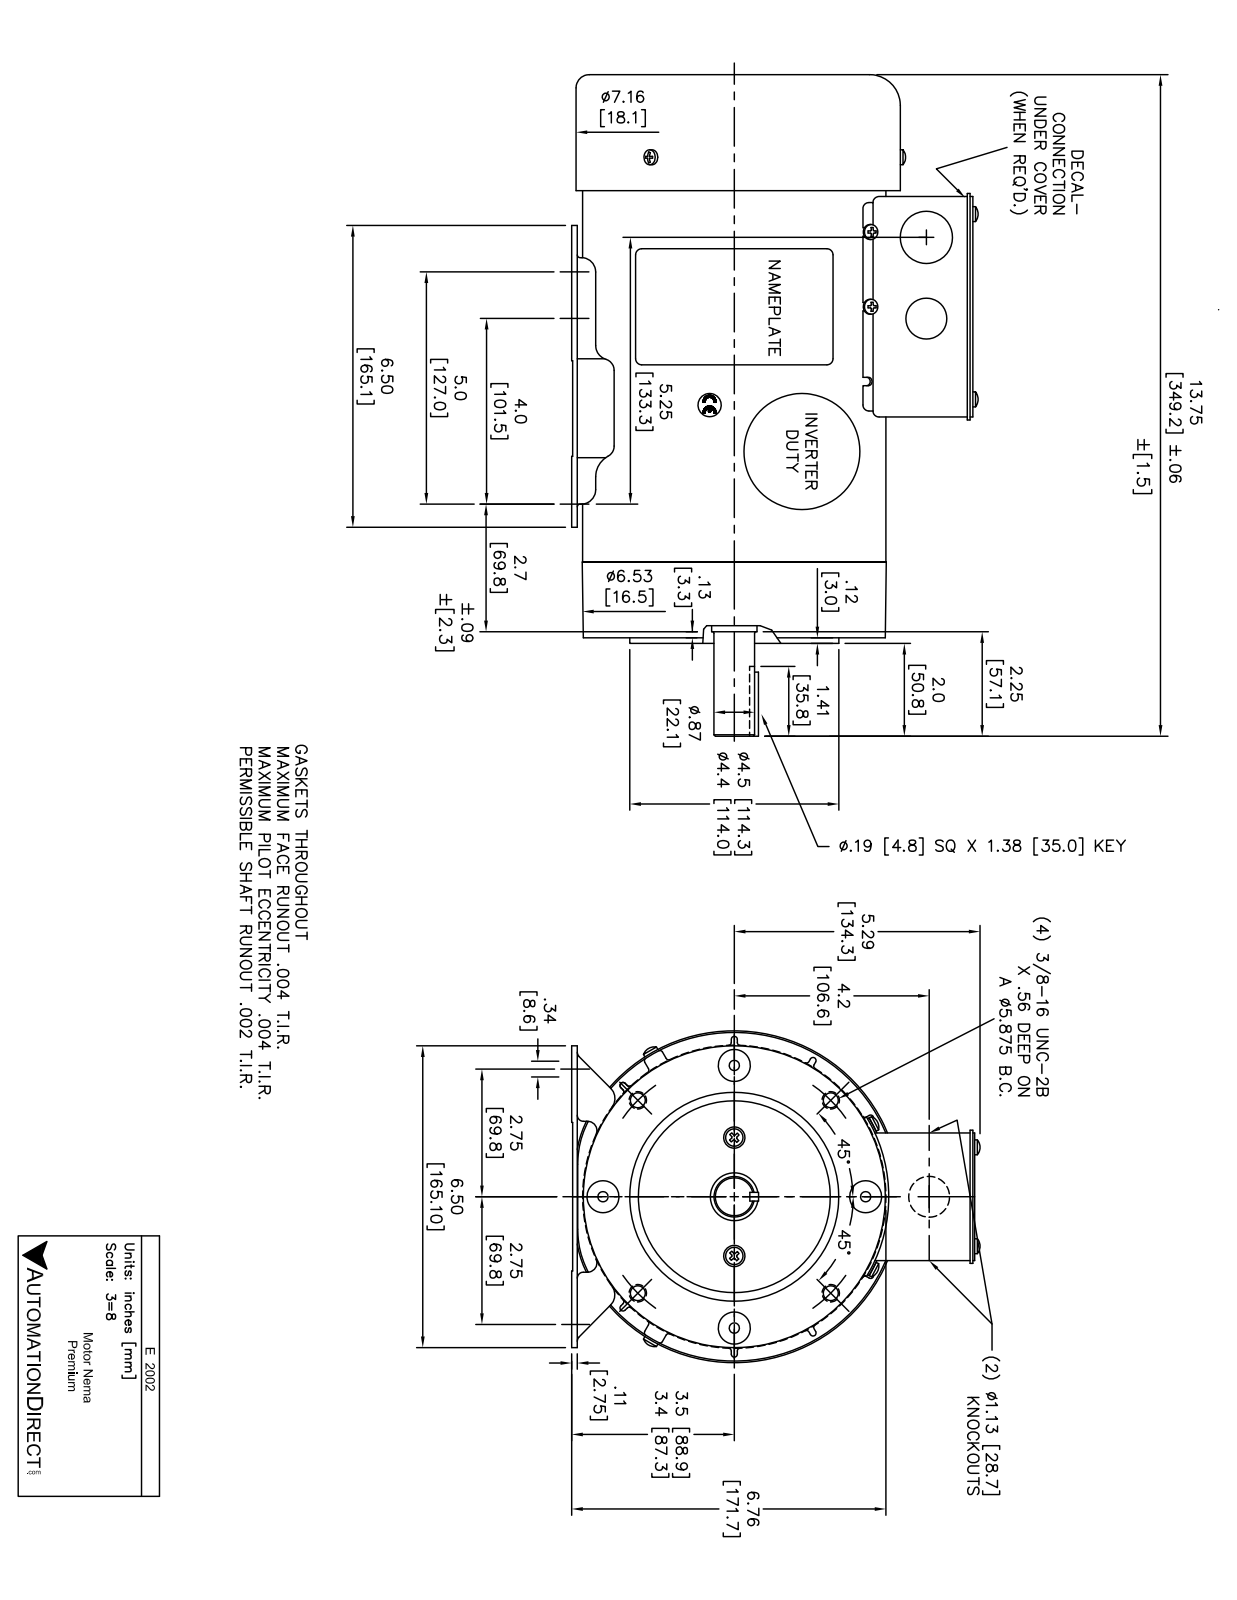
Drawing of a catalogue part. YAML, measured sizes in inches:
part_name: "028605-750_Rev02 red1 r1 w E2001A front bell"
step_written_by: "SolidWorks 2017 (AUTOMOTIVE_DESIGN)"
units: inches
bodies: {solids: 31, faces: 2645, planar: 1005, cylindrical: 940, other: 700}
overall_size: [13.755, 8.797, 7.148]
volume: 62
surface_area: 1045
round_holes:
  - {diameter: 0.22, count: 11}
  - {diameter: 0.19, count: 9}
  - {diameter: 0.147, count: 7}
  - {diameter: 0.34, count: 6}
  - {diameter: 0.125, count: 4}
  - {diameter: 0.128, count: 4}
  - {diameter: 0.138, count: 4}
  - {diameter: 0.163, count: 4}
  - {diameter: 0.271, count: 4}
  - {diameter: 0.313, count: 4}
  - {diameter: 0.103, count: 2}
  - {diameter: 0.173, count: 2}
round_bosses_or_shafts:
  - {diameter: 0.348, count: 9}
  - {diameter: 0.164, count: 9}
  - {diameter: 0.38, count: 4}
  - {diameter: 0.32, count: 4}
  - {diameter: 0.3, count: 3}
  - {diameter: 0.19, count: 3}
  - {diameter: 0.414, count: 2}
  - {diameter: 0.31, count: 2}
partial_cylinders:
  - {radius: 0.085, count: 144}
  - {radius: 0.06, count: 119}
  - {radius: 0.19, count: 20}
  - {radius: 0.17, count: 13}
  - {radius: 0.09, count: 12}
  - {radius: 0.2, count: 12}
  - {radius: 0.25, count: 10}
  - {radius: 0.065, count: 9}
face_to_face_distances: [0.035, 8.6, 0.015, 1.155, 1.19, 0.119, 0.11, 1.265, 1.3, 9.725]
hole_center_spacings: [3.26, 4.078, 4.147, 4.222, 4, 4.363, 4.195, 0.096]
